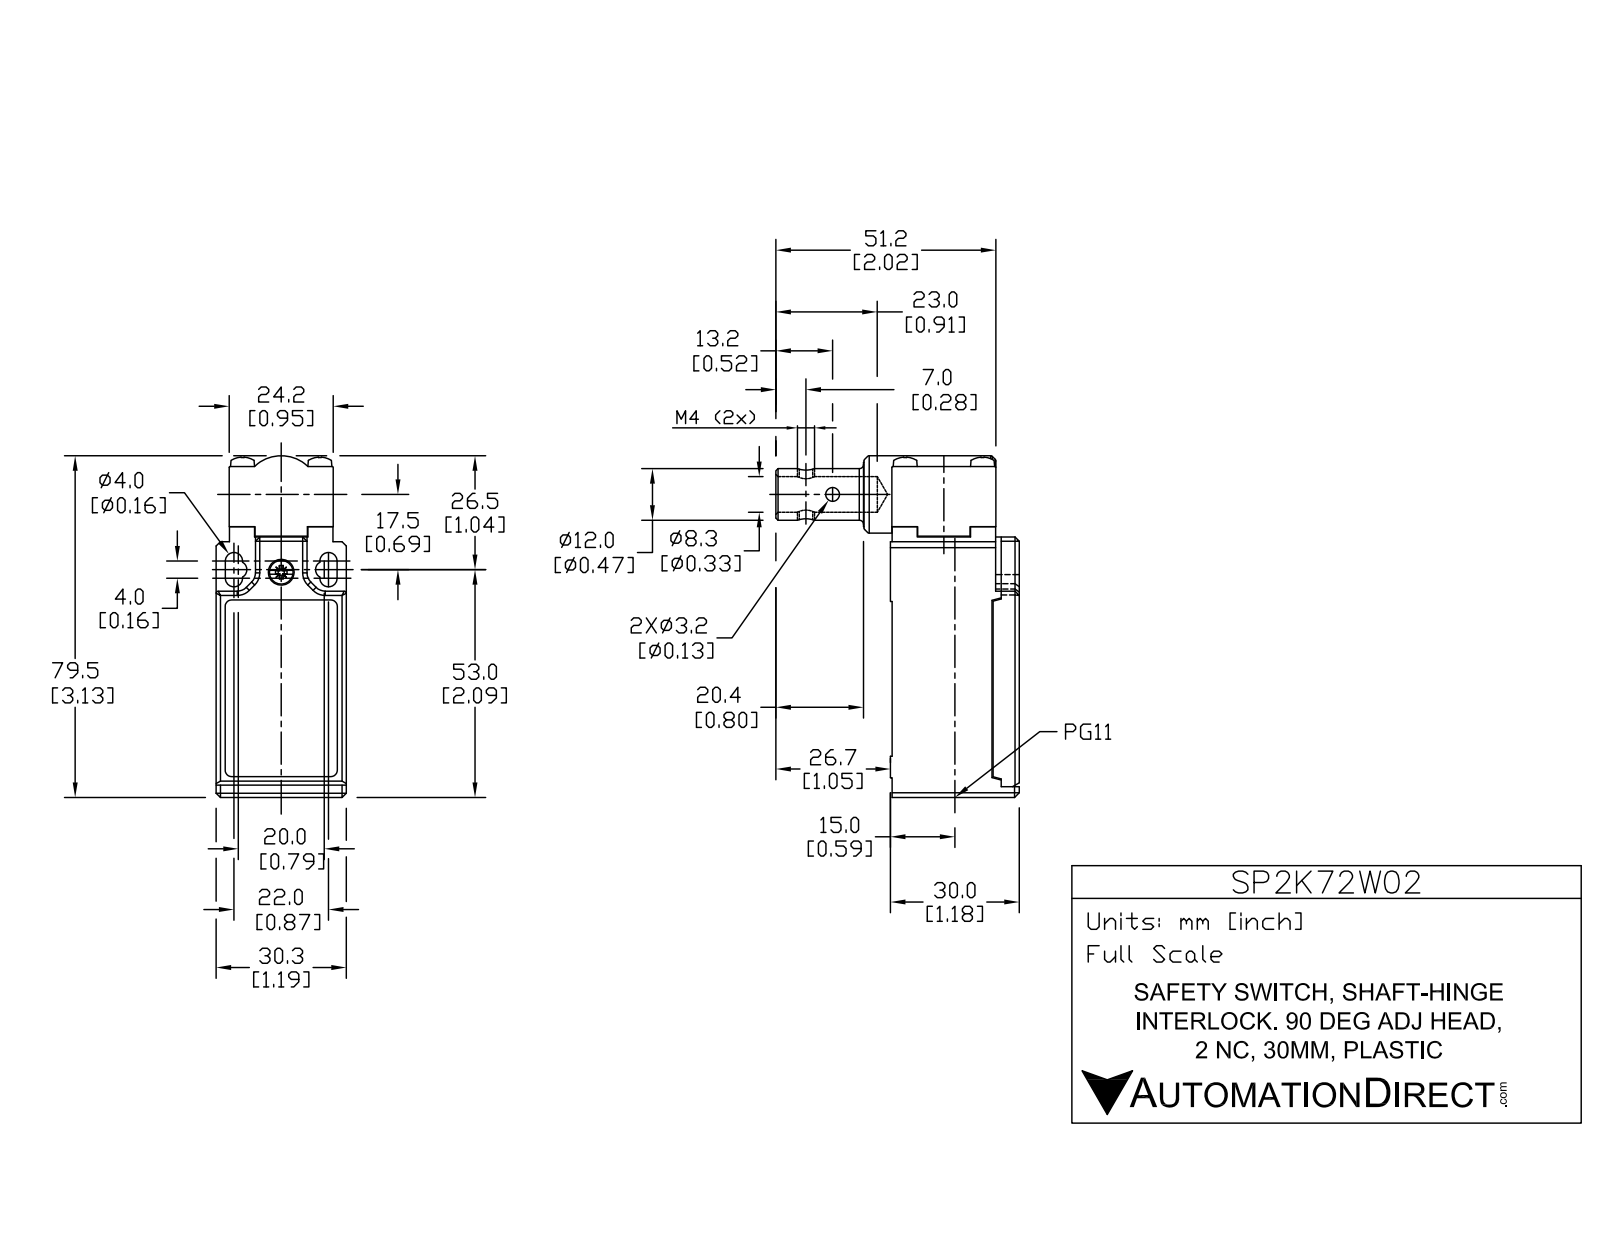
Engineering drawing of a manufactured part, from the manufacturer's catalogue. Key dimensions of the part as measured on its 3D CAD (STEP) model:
Part name (STEP PRODUCT): SP2K72W02
STEP written by: SolidWorks 2017 (AUTOMOTIVE_DESIGN)
Units: inches
Bodies: 3 solids, 200 faces (106 planar, 64 cylindrical, 30 other)
Overall size (bounding box): 3.15 × 2.255 × 1.193
Volume: 3.858 in³ · Surface area: 24.71 in²
Round holes (diameter × count): ⌀0.126 ×1, ⌀0.157 ×1, ⌀0.236 ×1, ⌀0.327 ×1, ⌀0.465 ×1, ⌀0.587 ×1, ⌀0.669 ×1, ⌀0.748 ×1
Round bosses / shafts (diameter × count): ⌀0.22 ×5, ⌀0.709 ×1, ⌀0.472 ×1
Partial cylindrical surfaces — rounded edges, fillets, slot ends (radius × count): R0.079 ×6, R0.02 ×4, R0.118 ×4, R0.394 ×1, R0.4 ×1
Main face-to-face distances: 1.193, 1.165, 0.945, 0.124, 1.069, 0.22, 2.406, 1.181, 0.961, 0.016
Hole centre spacings: 0.713, 1.102
